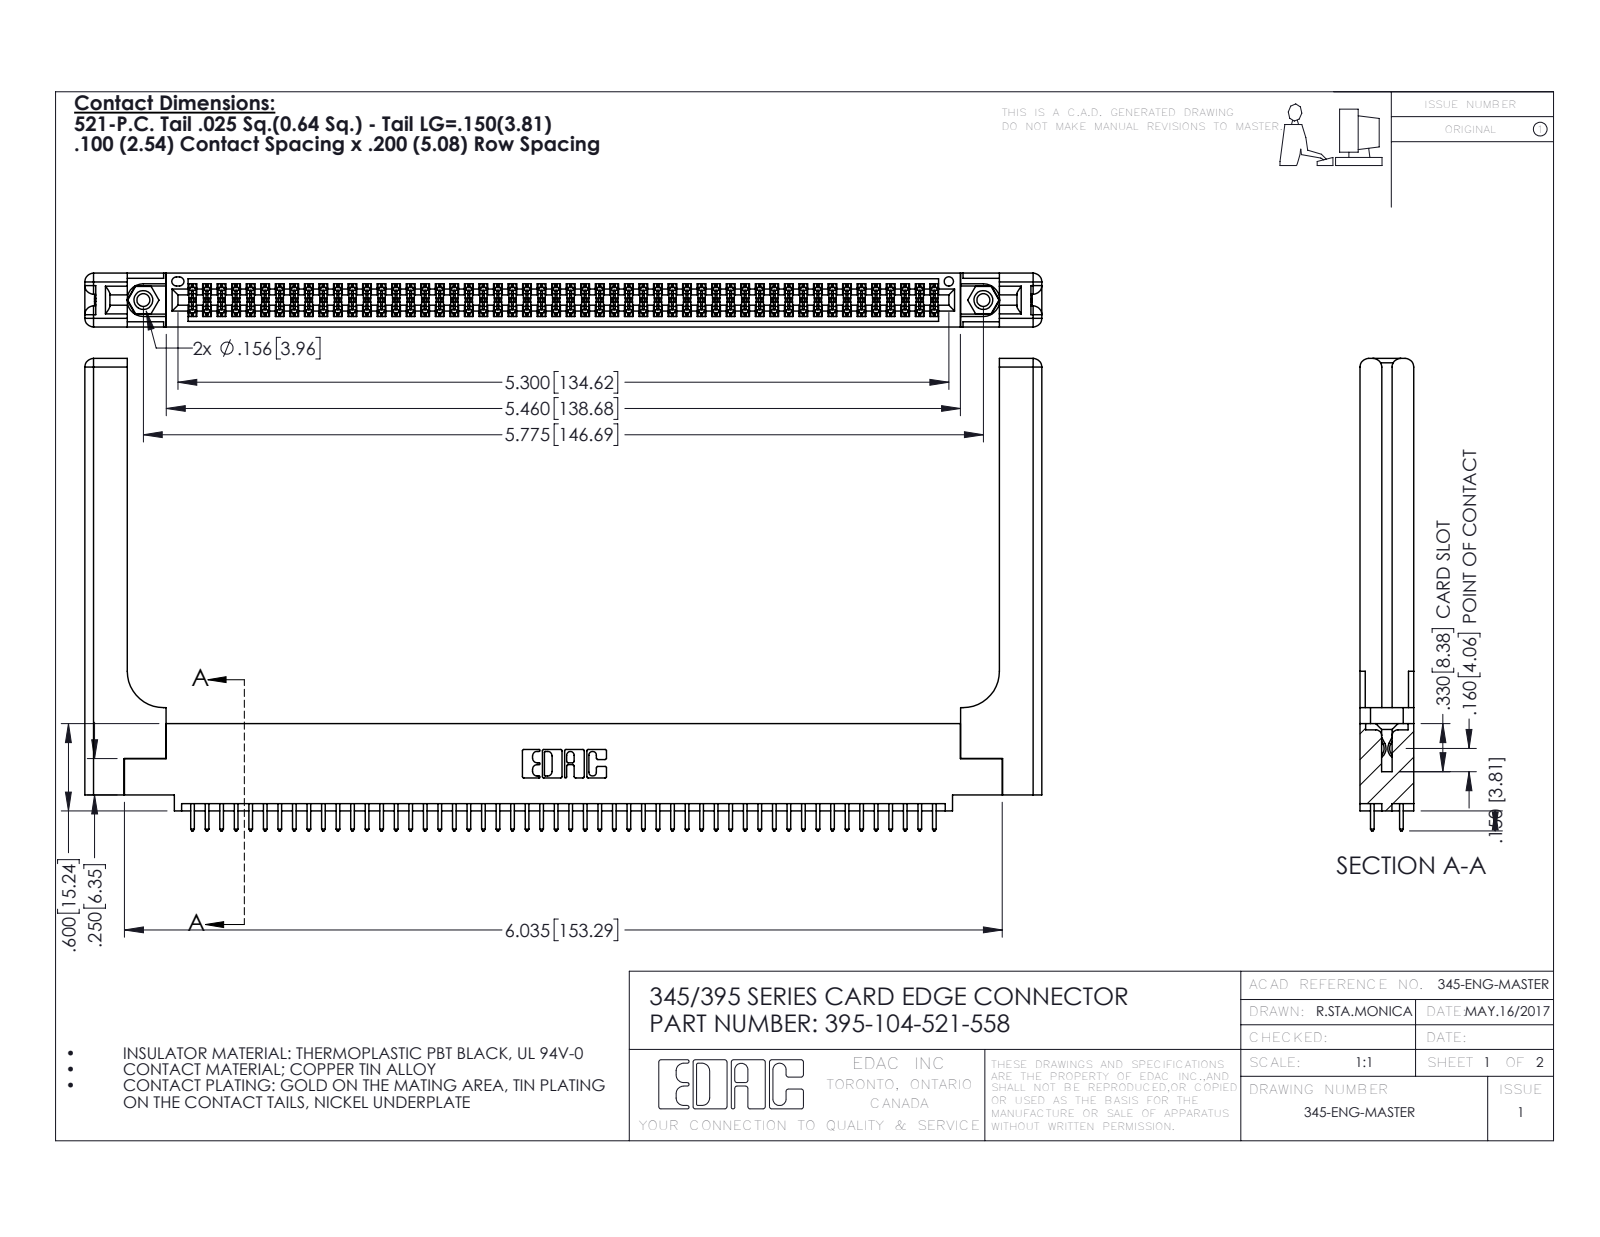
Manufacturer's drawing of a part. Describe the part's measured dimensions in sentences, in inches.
The part is named "345-220-058_345-220-058; 345 Part_0.110 Offset - 0.156 Dia-TH; 345-292-001_345-293-121; 395-104-521-558 (+1 more)". Its 3-D file was written by "SolidWorks 2016 (CONFIG_CONTROL_DESIGN)". It is 109 solids with 5586 faces: 3664 planar, 1862 cylindrical and 60 other. Overall it measures 6.579 by 3.247 by 0.37 inches. Its volume is 1.506 cubic inches and its surface area 45 square inches. Round holes: 2 of diameter 0.089, 2 of diameter 0.125, 2 of diameter 0.156, 1 of diameter 0.064. Round bosses or shafts: 2 of diameter 0.155. Partial cylindrical surfaces (rounded edges, fillets, slot ends): 156 of radius 0.006, 104 of radius 0.01, 22 of radius 0.01, 16 of radius 0.06, 6 of radius 0.007, 6 of radius 0.031, 3 of radius 0.026, 2 of radius 0.014. The main face-to-face distances are 0.072, 0.298, 0.37, 0.098, 0.272, 0.025, 0.2, 0.225, 0.148, 0.15. The hole center spacings are 0.27, 5.539, 5.775.
